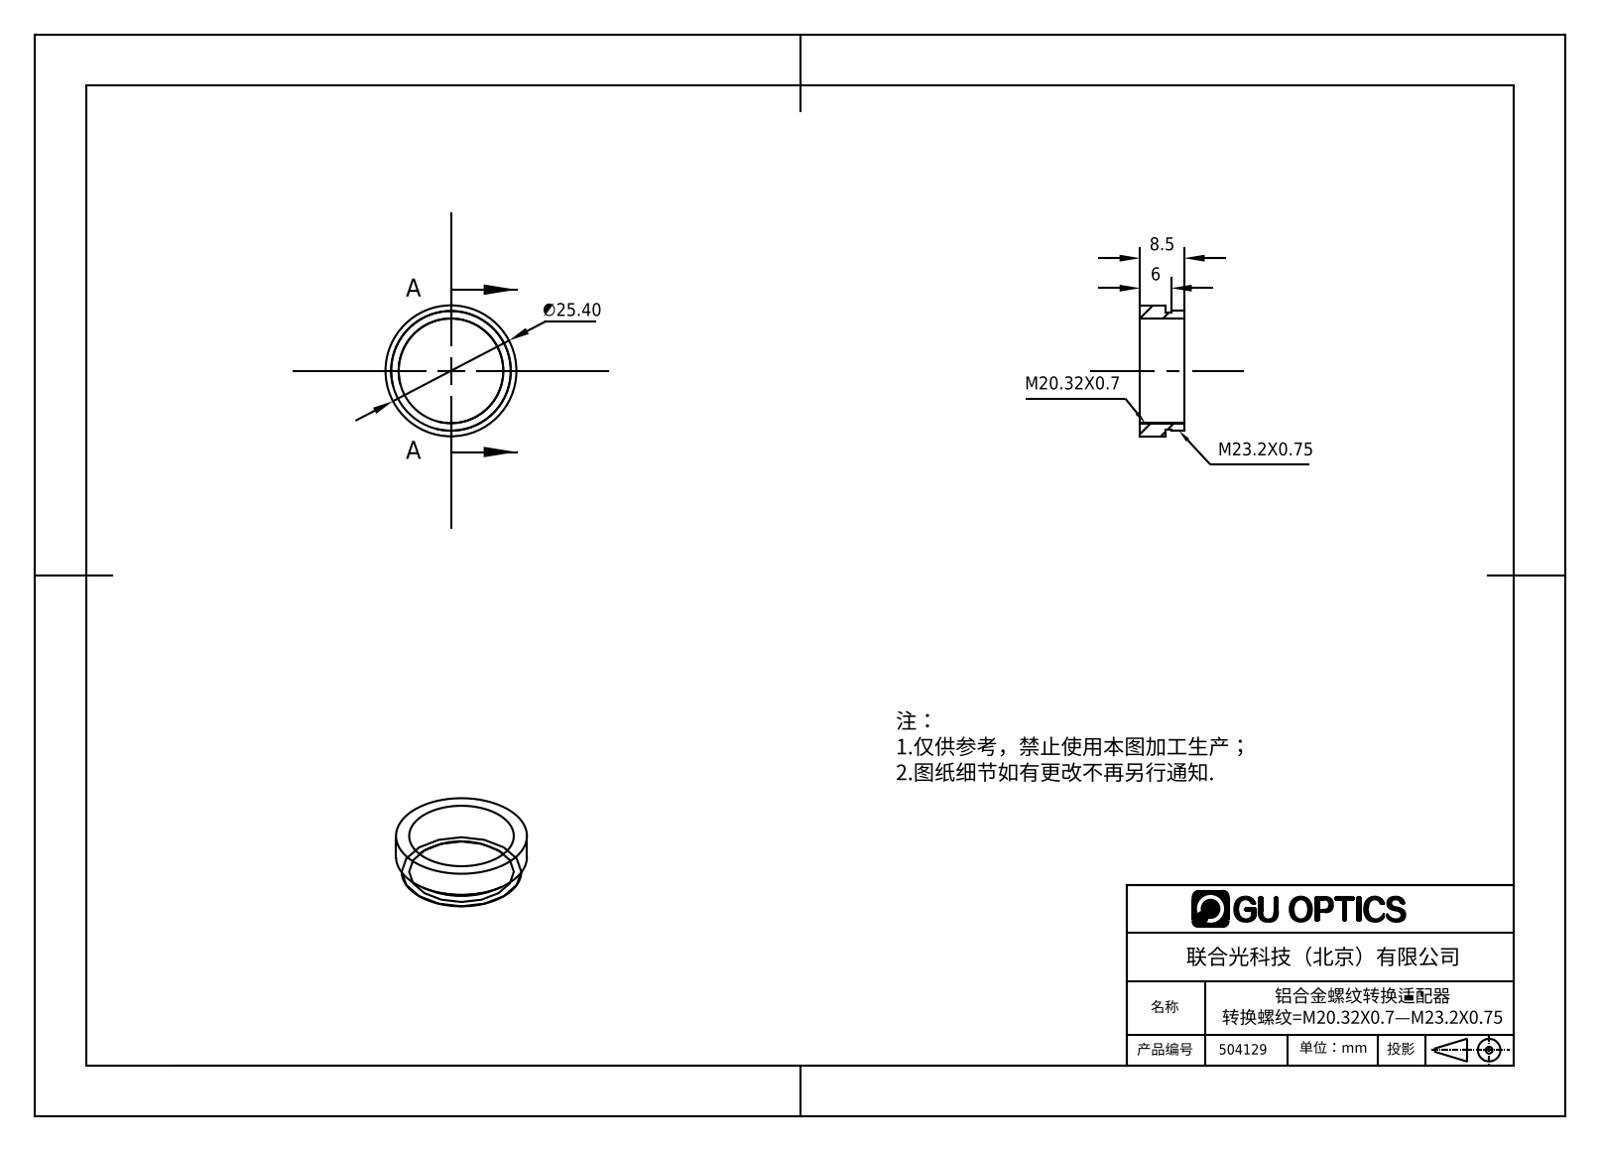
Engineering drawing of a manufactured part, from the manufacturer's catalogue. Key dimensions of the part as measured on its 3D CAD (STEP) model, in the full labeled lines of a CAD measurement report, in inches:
Part name (STEP PRODUCT): 504129
STEP written by: SolidWorks 2016 (AUTOMOTIVE_DESIGN)
Units: inches
Bodies: 1 solid, 12 faces (4 planar, 8 cylindrical, 0 other)
Overall size (bounding box): 1 × 1 × 0.335
Volume: 0.076 in³ · Surface area: 2.477 in²
Round holes (diameter × count): ⌀0.799 ×1
Round bosses / shafts (diameter × count): ⌀1 ×1, ⌀0.914 ×1, ⌀0.894 ×1
Main face-to-face distances: 0.197, 0.138, 0.335, 0.098, 0.039, 0.236
